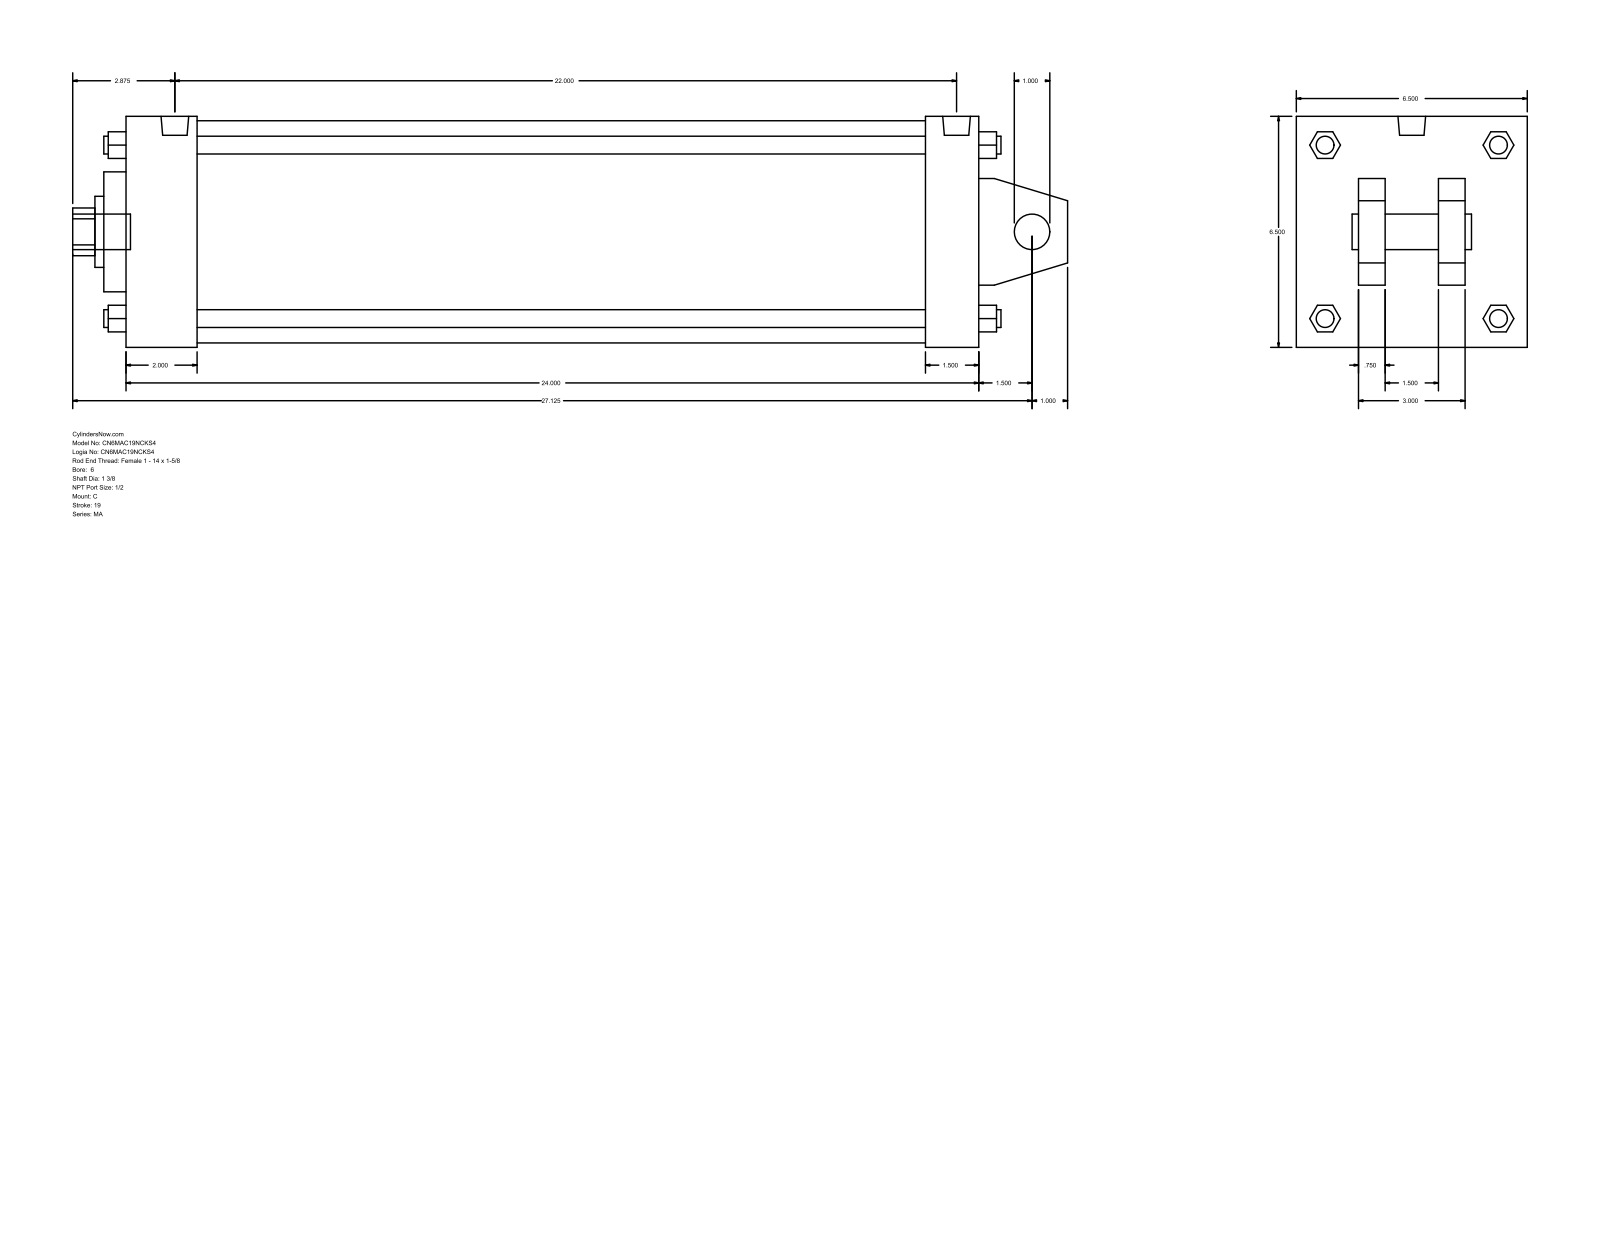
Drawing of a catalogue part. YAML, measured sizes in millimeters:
part_name: "MA_C__0600_1.375"
step_written_by: "GSSL Pune (CONFIG_CONTROL_DESIGN)"
units: millimeters
bodies: {solids: 0, faces: 141, planar: 109, cylindrical: 32, other: 0}
overall_size: [711.2, 165.1, 165.1]
round_holes:
  - {diameter: 25.4, count: 1}
  - {diameter: 34.92, count: 1}
  - {diameter: 50.8, count: 1}
  - {diameter: 85.72, count: 1}
  - {diameter: 158.75, count: 1}
round_bosses_or_shafts:
  - {diameter: 17.46, count: 4}
  - {diameter: 12.7, count: 4}
  - {diameter: 19.77, count: 2}
  - {diameter: 25.4, count: 1}
partial_cylinders:
  - {radius: 17.06, count: 1}
face_to_face_distances: [165.1, 609.6, 38.1, 19.05, 63.5, 101.6, 50.8, 44.45, 120.65, 571.5]
